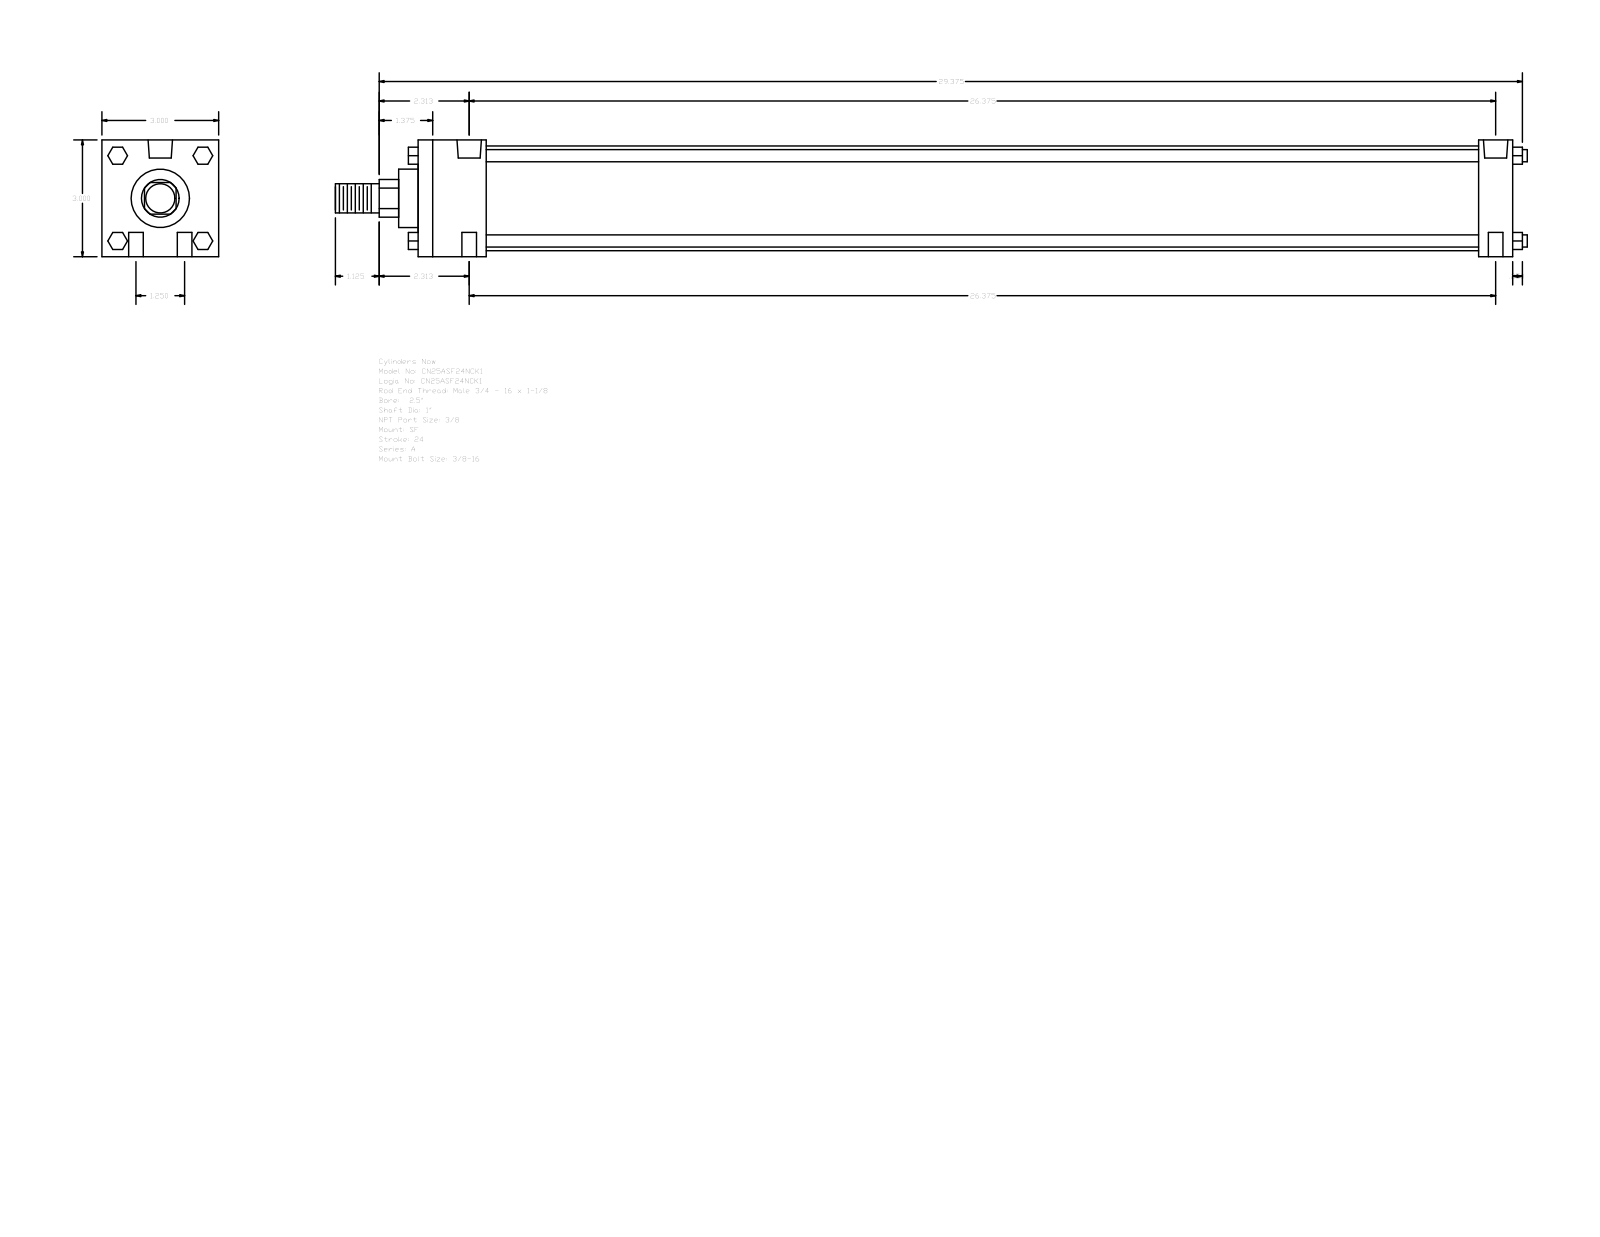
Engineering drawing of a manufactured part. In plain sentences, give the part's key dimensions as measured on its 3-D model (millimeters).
The part is named "A_SF__0250_1". Its 3-D file was written by "GSSL Pune (CONFIG_CONTROL_DESIGN)". It is 0 solids with 124 faces: 94 planar, 30 cylindrical and 0 other. Overall it measures 777.88 by 76.2 by 76.2 millimeters. Round holes: 4 of diameter 9.53, 2 of diameter 5.56, 2 of diameter 15.93. Round bosses or shafts: 4 of diameter 7.94, 1 of diameter 68.33, 1 of diameter 38.1, 1 of diameter 25.4, 1 of diameter 19.05. Partial cylindrical surfaces (rounded edges, fillets, slot ends): 1 of radius 12.29. The main face-to-face distances are 76.2, 714.37, 692.15, 22.22, 44.45, 647.7, 669.92, 12.7, 727.07, 6.35. The hole center spacings are 15.88, 670.11, 669.92, 31.76, 670.67, 674.68.
